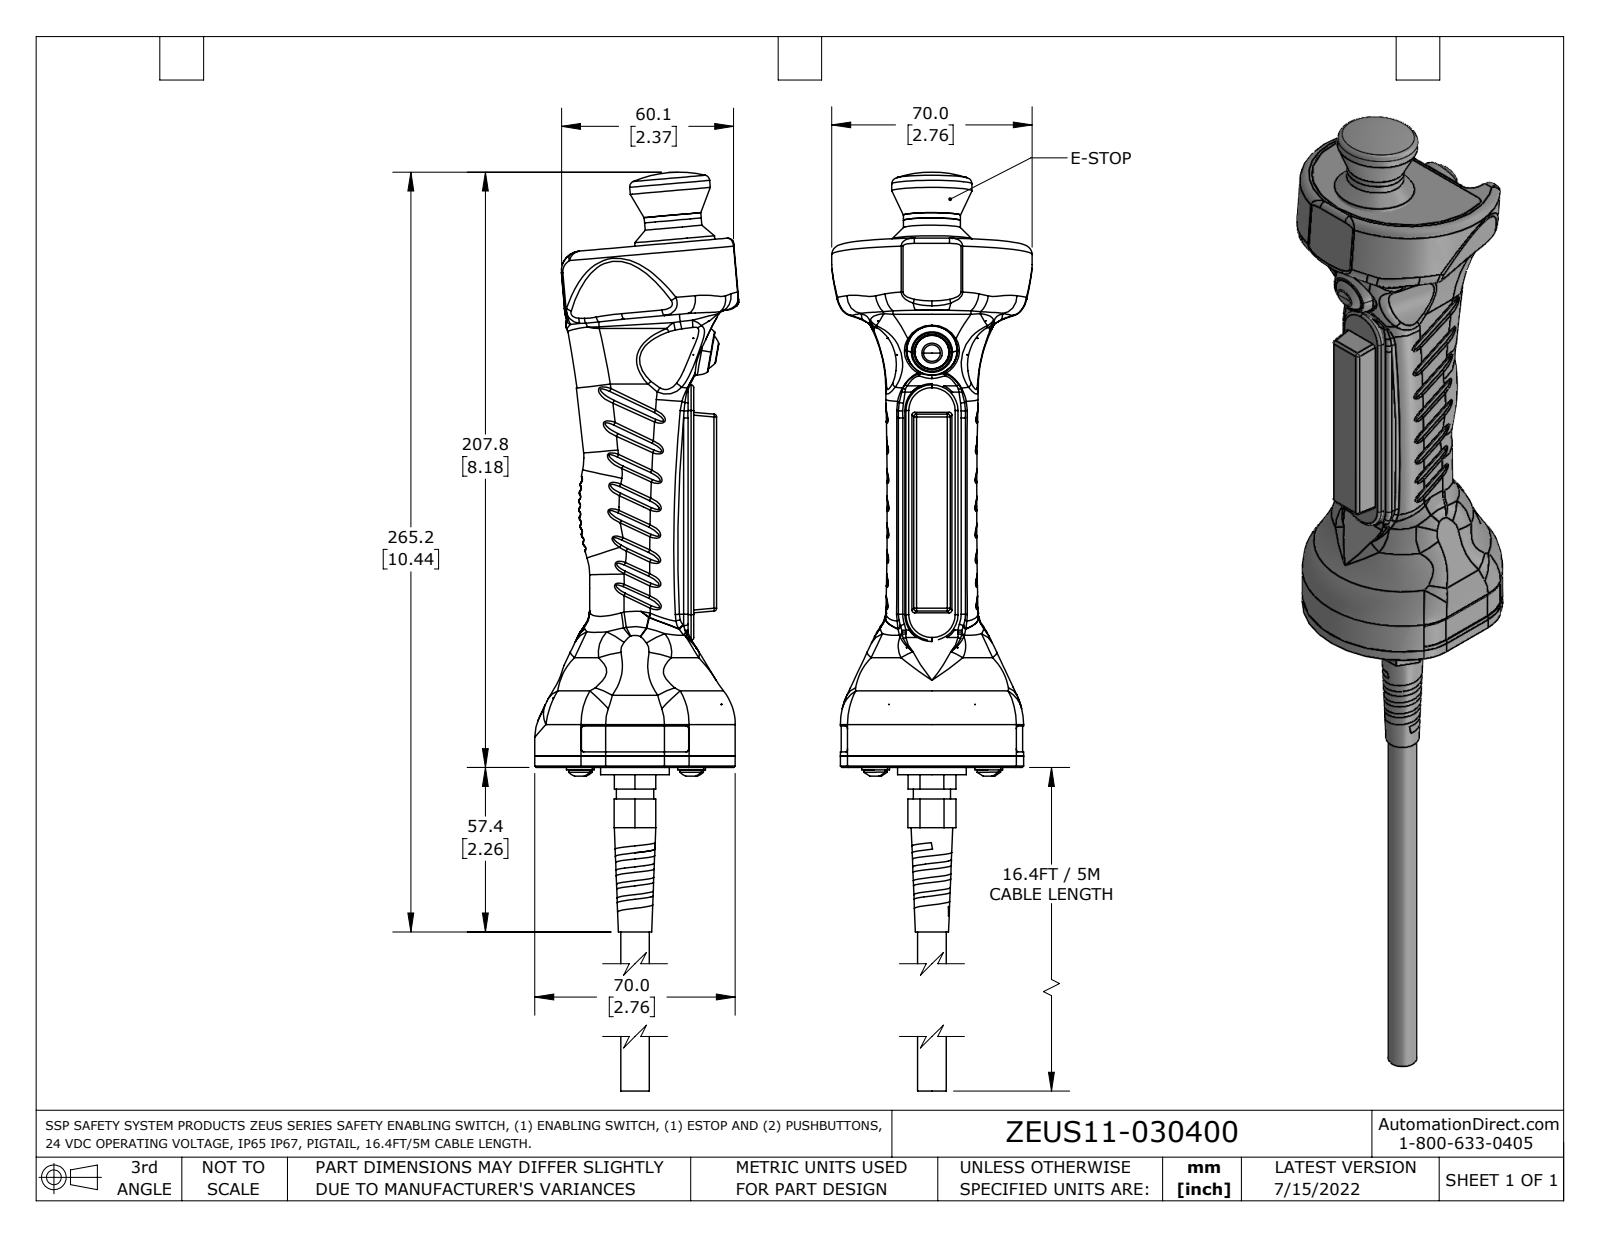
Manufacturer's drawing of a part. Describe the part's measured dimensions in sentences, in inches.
The part is named "ZEUS11-030400". Its 3-D file was written by "SolidWorks 2021 (AUTOMOTIVE_DESIGN)". It is 22 solids with 1627 faces: 628 planar, 516 cylindrical and 483 other. Overall it measures 15.833 by 2.803 by 2.756 inches. Its volume is 24.79 cubic inches and its surface area 140.1 square inches. Round holes: 4 of diameter 0.132, 4 of diameter 0.169, 4 of diameter 0.177, 4 of diameter 0.197, 2 of diameter 0.039, 2 of diameter 0.098, 2 of diameter 0.11, 2 of diameter 0.159, 2 of diameter 0.165, 2 of diameter 0.201, 2 of diameter 0.205, 2 of diameter 0.299. Round bosses or shafts: 4 of diameter 0.354, 4 of diameter 0.295, 4 of diameter 0.157, 4 of diameter 0.039, 3 of diameter 0.461, 2 of diameter 1.102, 2 of diameter 0.781, 2 of diameter 0.689. Partial cylindrical surfaces (rounded edges, fillets, slot ends): 96 of radius 0.005, 51 of radius 0.039, 48 of radius 0.028, 42 of radius 0.008, 21 of radius 0.079, 16 of radius 0.006, 10 of radius 0.118, 7 of radius 0.031. The main face-to-face distances are 0.157, 0.079, 0.02, 0.014, 0.065, 0.059, 0.098, 0.039, 0.177, 0.571. The hole center spacings are 0.404, 0.867, 1.08, 1.181, 0.63, 1.531, 1.558, 0.513.
